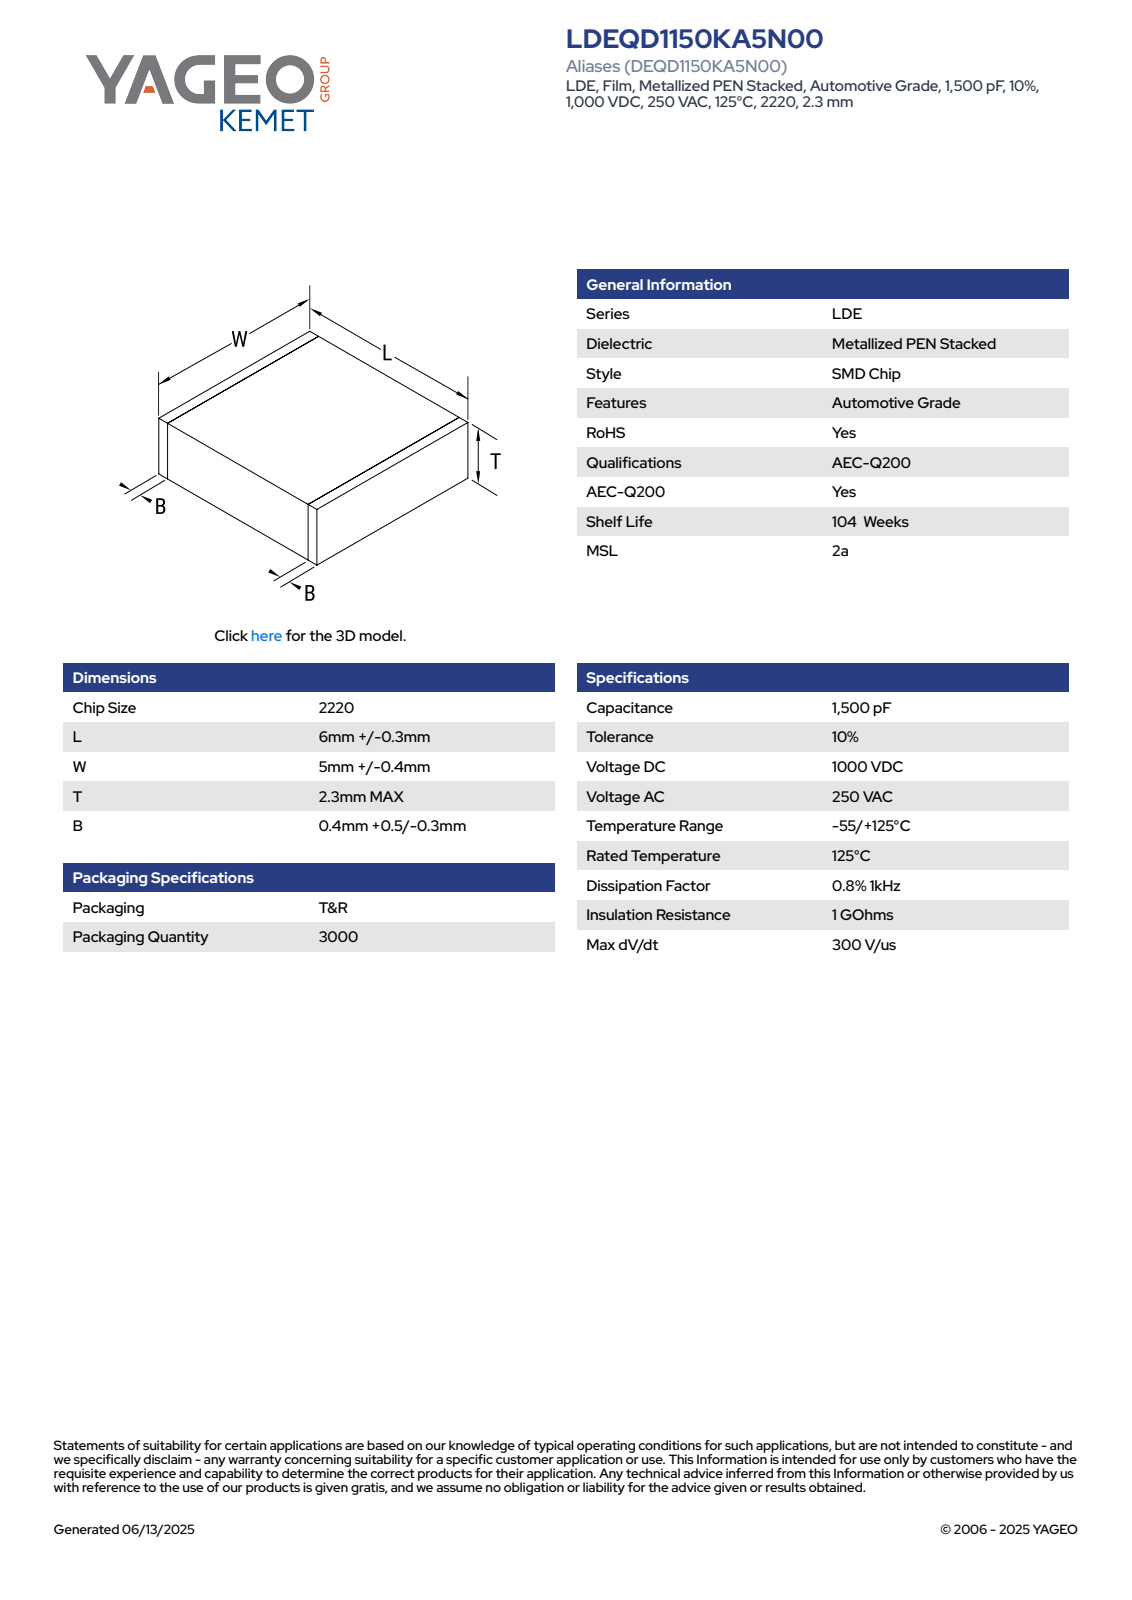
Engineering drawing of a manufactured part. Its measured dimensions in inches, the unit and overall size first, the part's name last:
Units: inches
Overall size (bounding box): 0.248 × 0.213 × 0.091
Main face-to-face distances: 0.09, 0.248, 0.212, 0.09, 0.091, 0.212, 0.213, 0.02, 0.228, 0.209
Volume: 0.005 in³ · Surface area: 0.192 in²
Bodies: 4 solids, 73 faces (73 planar, 0 cylindrical, 0 other)
Part name (STEP PRODUCT): CFS_LDELDB_2220_L6.3W5.4T2.3B0.9
STEP written by: SolidWorks 2020 (AUTOMOTIVE_DESIGN)
